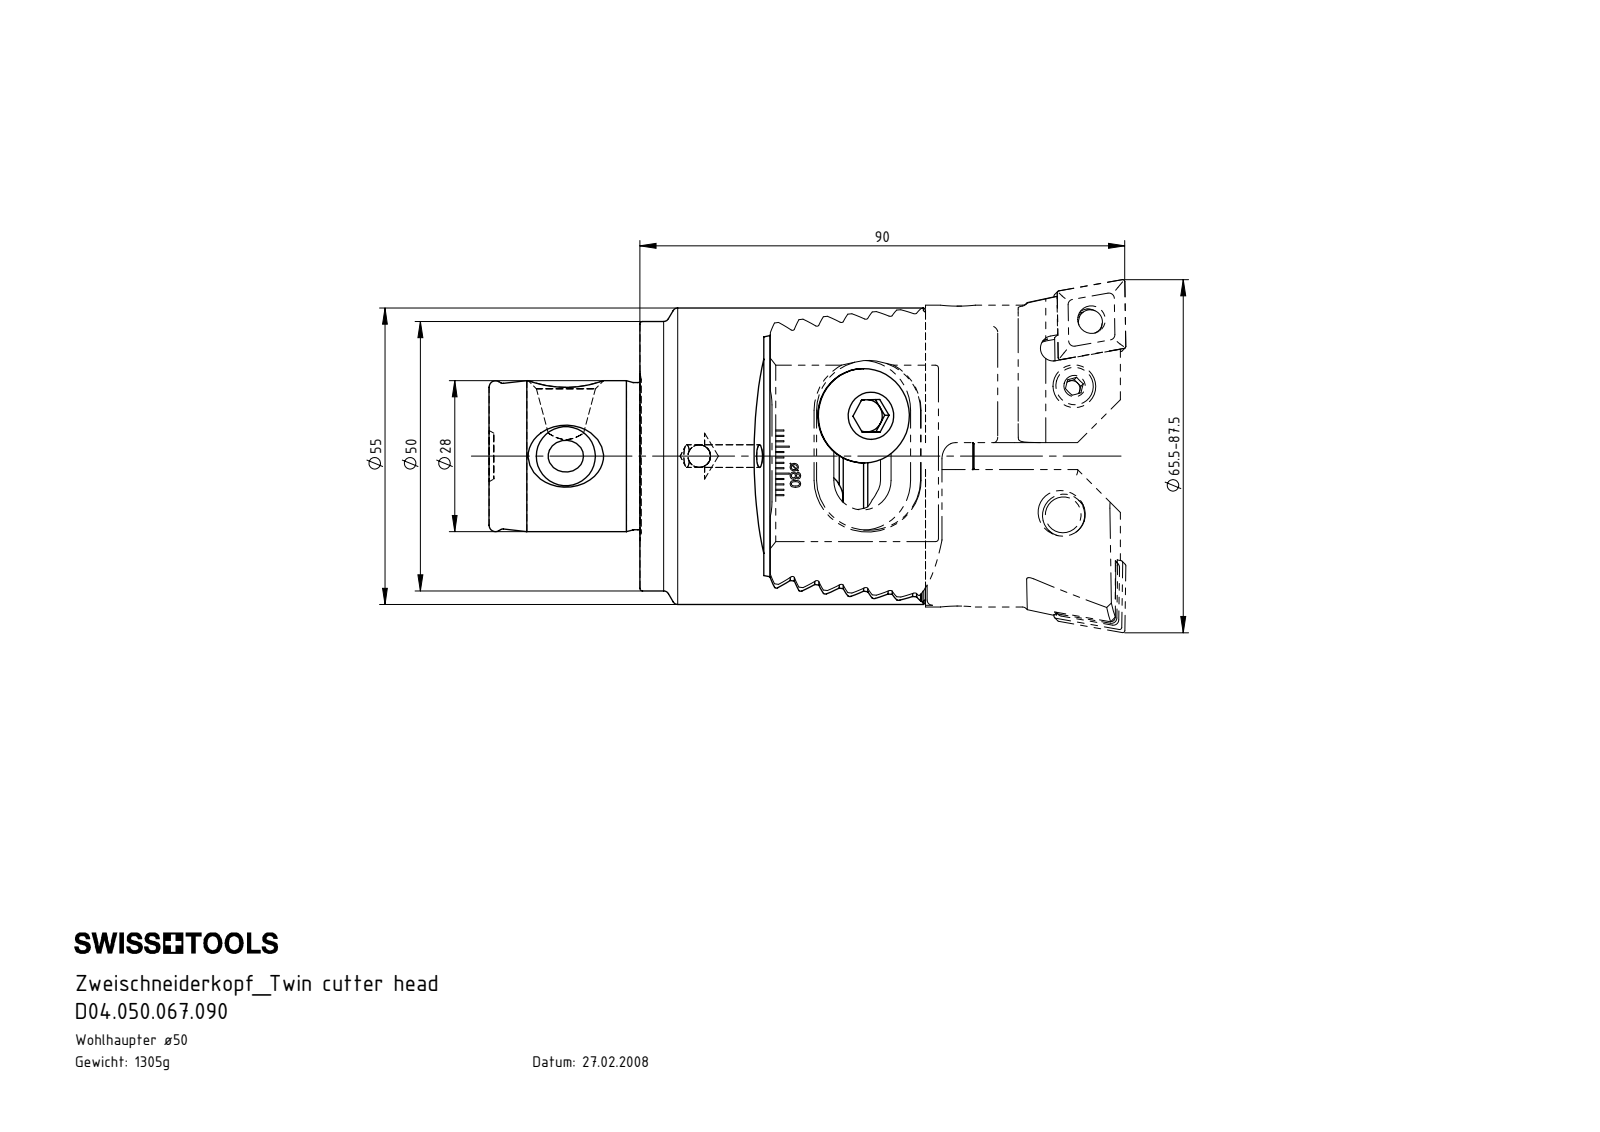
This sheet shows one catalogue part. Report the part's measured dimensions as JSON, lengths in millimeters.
{"part_name": "WH5.Z55.K23.090; Z55-WCD.101.037; Z55-ER3.001.020; CNMG120404 (+8 more)", "step_written_by": "SolidWorks 2012 (CONFIG_CONTROL_DESIGN)", "units": "millimeters", "bodies": {"solids": 20, "faces": 1200, "planar": 575, "cylindrical": 259, "other": 366}, "overall_size": [118.19, 65.5, 55], "volume_mm3": 165481, "surface_area_mm2": 49708, "round_holes": [[4.2, 3], [8.5, 3], [2, 2], [5.16, 2], [6.4, 2], [7, 2], [8.4, 2], [10.5, 2], [11, 2], [3.3, 1], [5, 1]], "round_bosses_or_shafts": [[17.5, 2], [17, 2], [10, 2], [8, 2], [7.9, 2], [6.4, 2], [4.5, 2], [4, 2]], "partial_cylinders_radius": [[1, 22], [0.34, 14], [0.34, 12], [0.4, 8], [2.5, 6], [3, 6], [5.5, 4], [9.25, 4]], "face_to_face_distances": [4.07, 8.14, 12.21, 16.28, 4.11, 20.35, 4.03, 4.01, 8.18, 4.13], "hole_center_spacings": [12.8, 12.86, 16, 30.9]}
